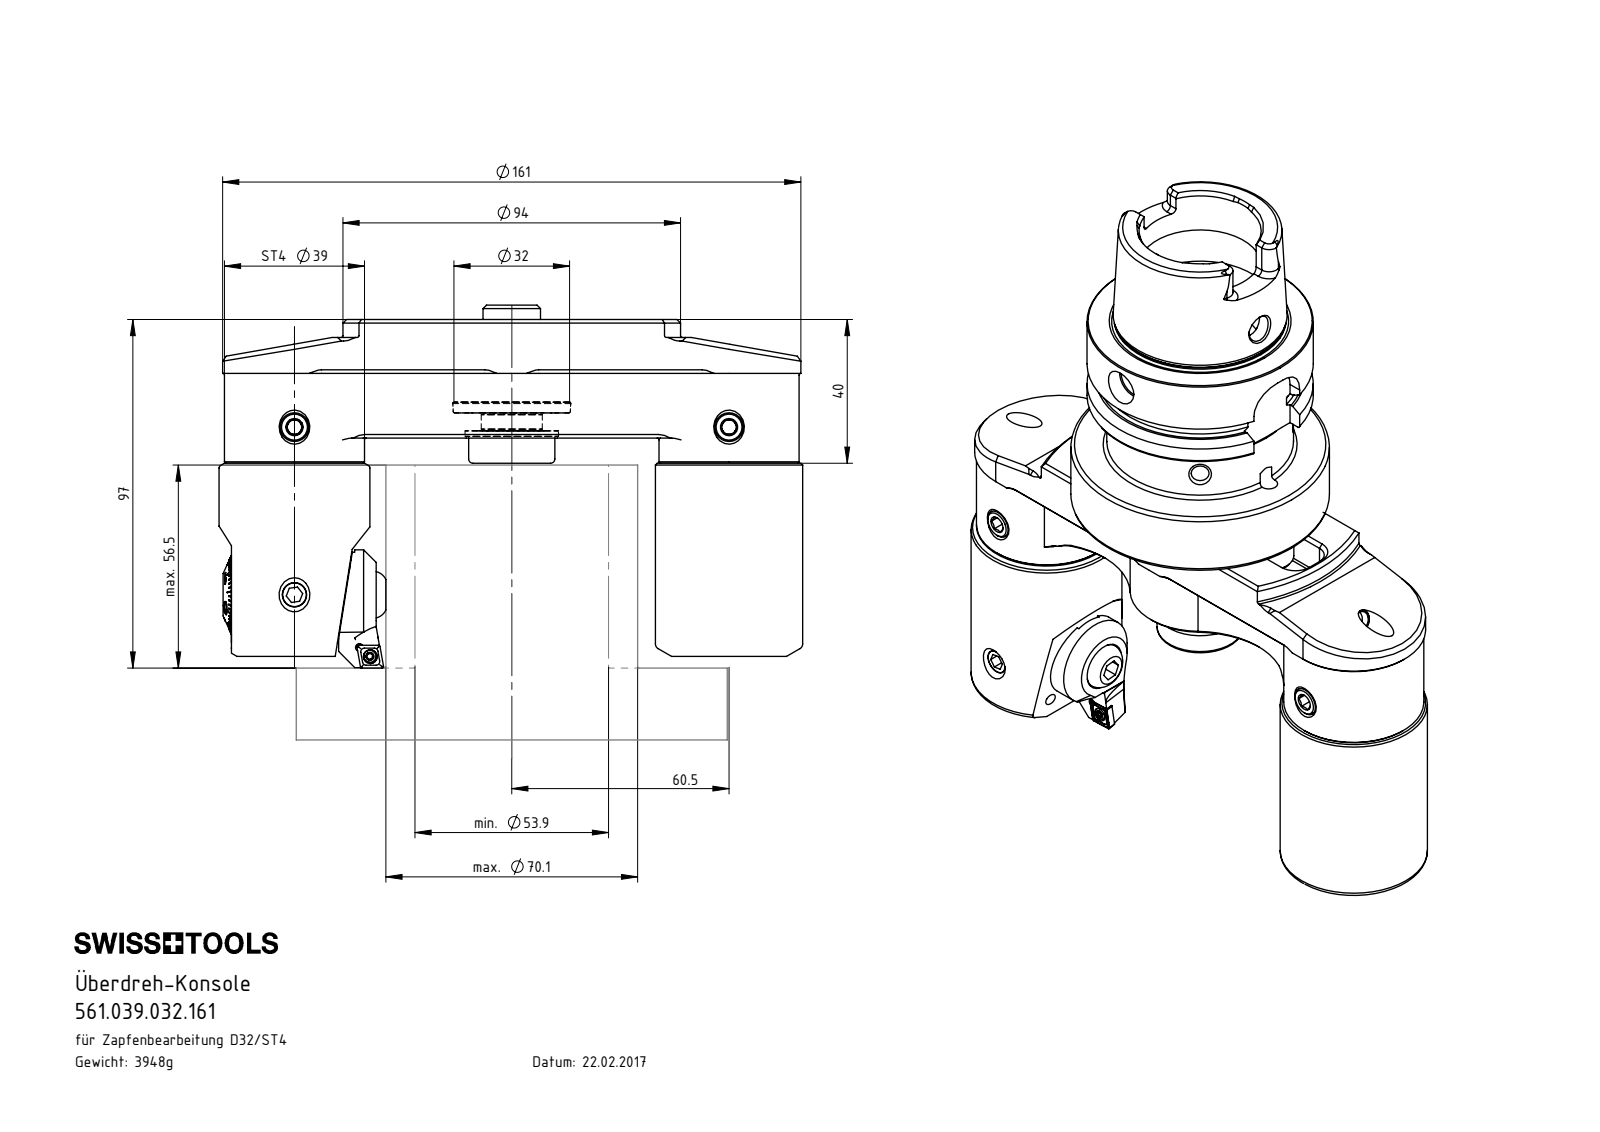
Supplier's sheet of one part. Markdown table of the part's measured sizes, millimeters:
| quantity | value |
| --- | --- |
| part name | KoU-D32.ST4.161_C_KoU-D32.WN5.212; ST4-ER2.001.009_A; ST4-ER1.001.011_A; KoU.D32.ST4.161 (+4 more) |
| STEP written by | SolidWorks 2017 (AUTOMOTIVE_DESIGN) |
| units | millimeters |
| bodies | 11 solids, 343 faces (125 planar, 72 cylindrical, 146 other) |
| overall size | 161.5 × 97.75 × 41 |
| volume | 199 395 mm³ |
| surface area | 52 400 mm² |
| round holes (diameter × count) | 5 × 5, 3.5 × 2, 4 × 2, 6 × 2, 7.25 × 2, 22 × 2, 23 × 2, 2 × 1, 10.2 × 1, 17 × 1, 26 × 1, 32 × 1 |
| round bosses / shafts (diameter × count) | 39 × 2, 8 × 2, 6 × 2, 41 × 1, 24 × 1, 21.8 × 1, 21.3 × 1, 16 × 1 |
| partial cylindrical surfaces (radius × count) | 0.5 × 8, 3.2 × 4, 4.5 × 4, 24.63 × 4, 3.48 × 2, 11.05 × 2, 20 × 2, 19.5 × 1 |
| main face-to-face distances | 40, 5, 7, 15, 15.5, 25, 18, 33, 16, 10 |
| hole center spacings | 121, 13.2, 60.5, 0.35, 26.4, 47.3, 73.7, 107.8 |
